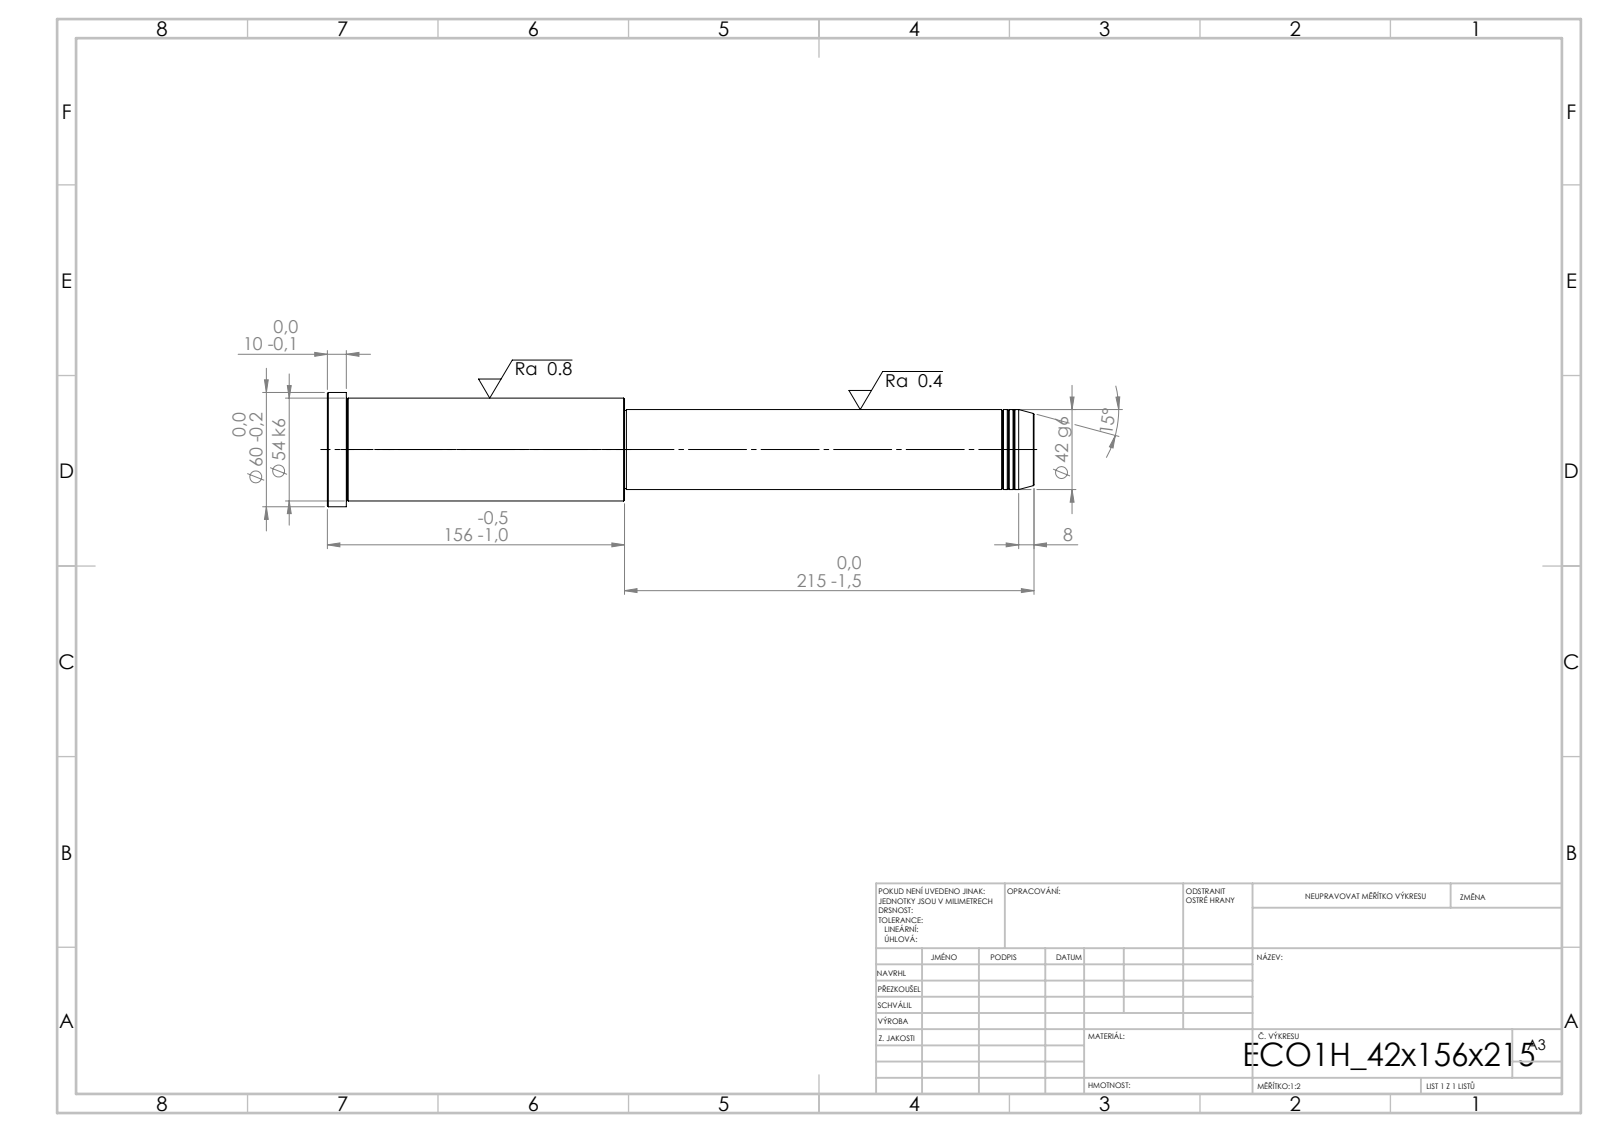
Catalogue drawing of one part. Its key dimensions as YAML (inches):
step_written_by: "SolidWorks 2019 (CONFIG_CONTROL_DESIGN)"
units: inches
bodies: {solids: 1, faces: 43, planar: 5, cylindrical: 14, other: 24}
overall_size: [14.606, 2.362, 2.362]
volume: 40.22
surface_area: 94.1
round_bosses_or_shafts:
  - {diameter: 2.362, count: 1}
  - {diameter: 2.126, count: 1}
  - {diameter: 1.654, count: 1}
  - {diameter: 1.614, count: 1}
face_to_face_distances: [14.606, 8.465, 6.142, 14.213, 5.748, 0.394, 8.425, 0.039, 5.787, 6.181]
